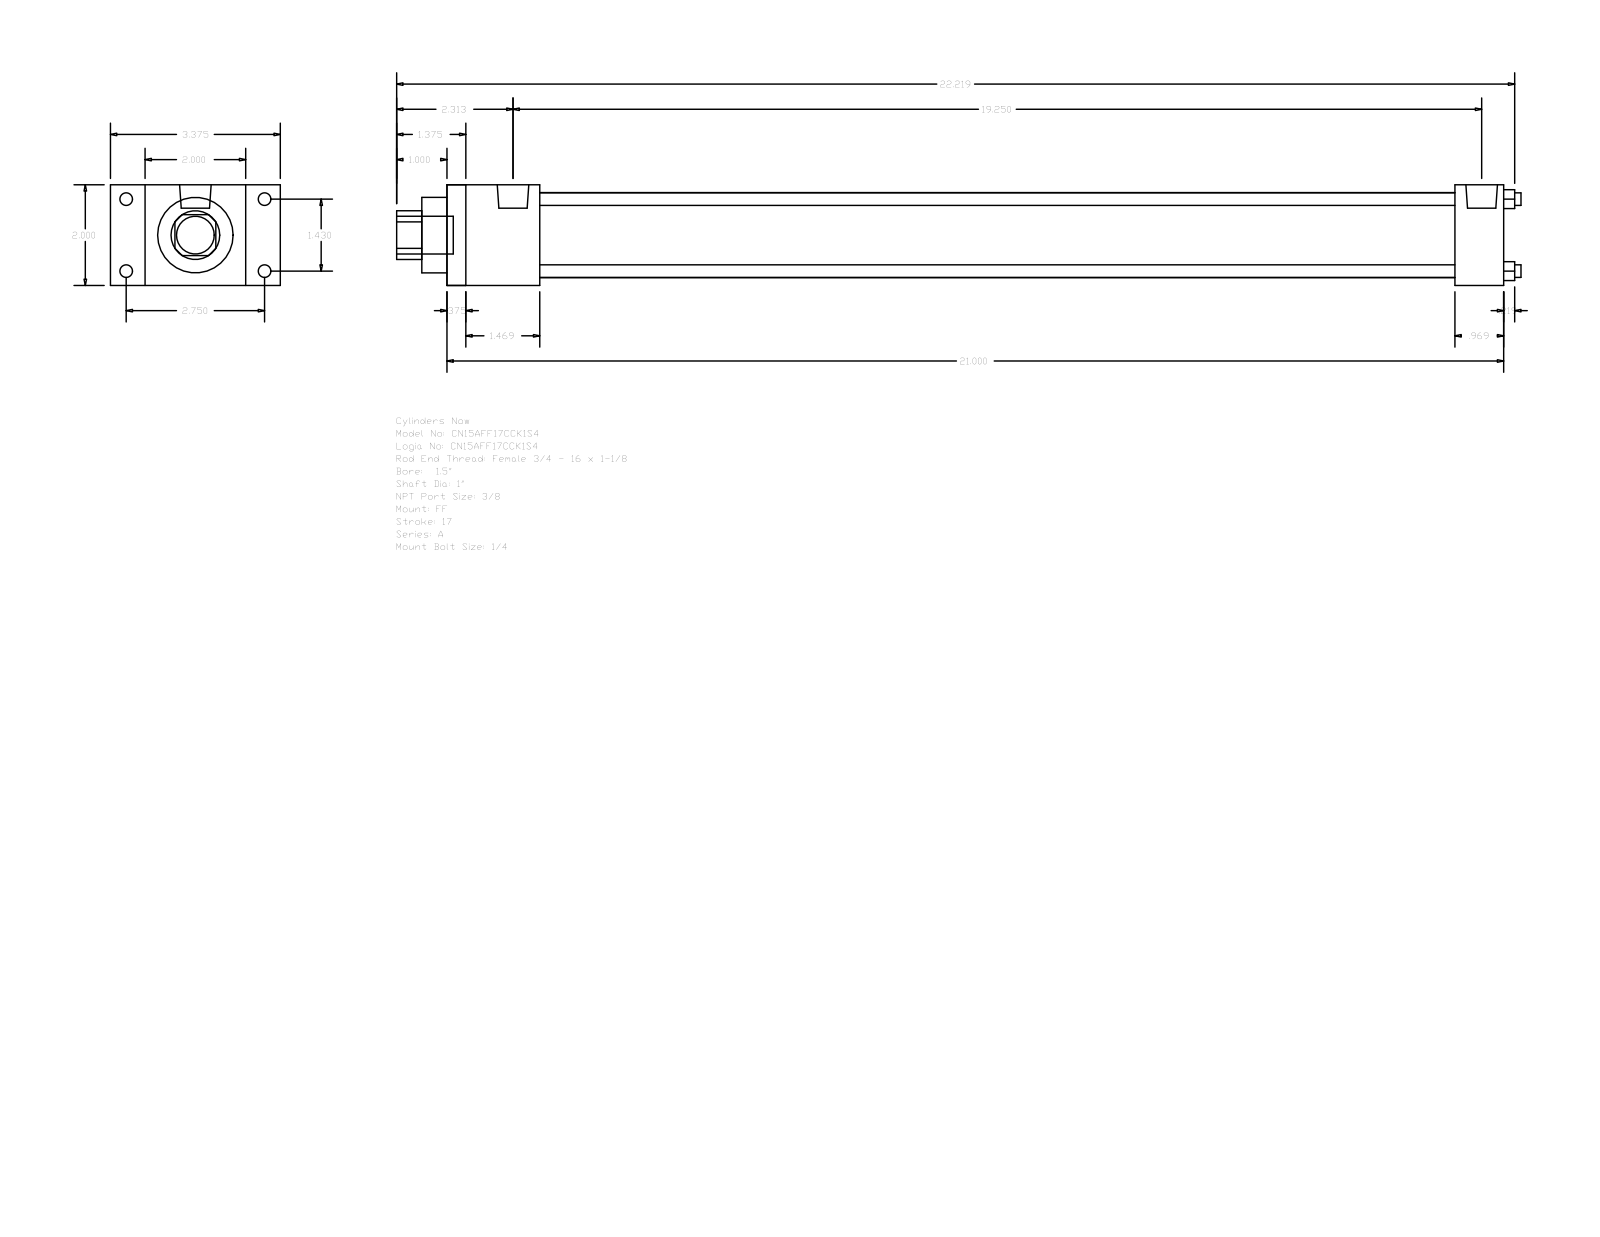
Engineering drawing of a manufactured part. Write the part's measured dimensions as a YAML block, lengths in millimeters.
part_name: "A_FF__0150_1"
step_written_by: "GSSL Pune (CONFIG_CONTROL_DESIGN)"
units: millimeters
bodies: {solids: 0, faces: 92, planar: 64, cylindrical: 28, other: 0}
overall_size: [567.53, 85.72, 50.8]
round_holes:
  - {diameter: 6.35, count: 4}
  - {diameter: 25.4, count: 1}
  - {diameter: 38.1, count: 1}
  - {diameter: 42.93, count: 1}
round_bosses_or_shafts:
  - {diameter: 6.35, count: 4}
  - {diameter: 5.56, count: 4}
  - {diameter: 15.93, count: 2}
  - {diameter: 19.05, count: 1}
partial_cylinders:
  - {radius: 12.29, count: 1}
face_to_face_distances: [50.8, 533.4, 9.52, 523.88, 46.83, 508.79, 37.31, 499.27, 461.96, 486.57]
hole_center_spacings: [25.68, 36.32, 51.36]
